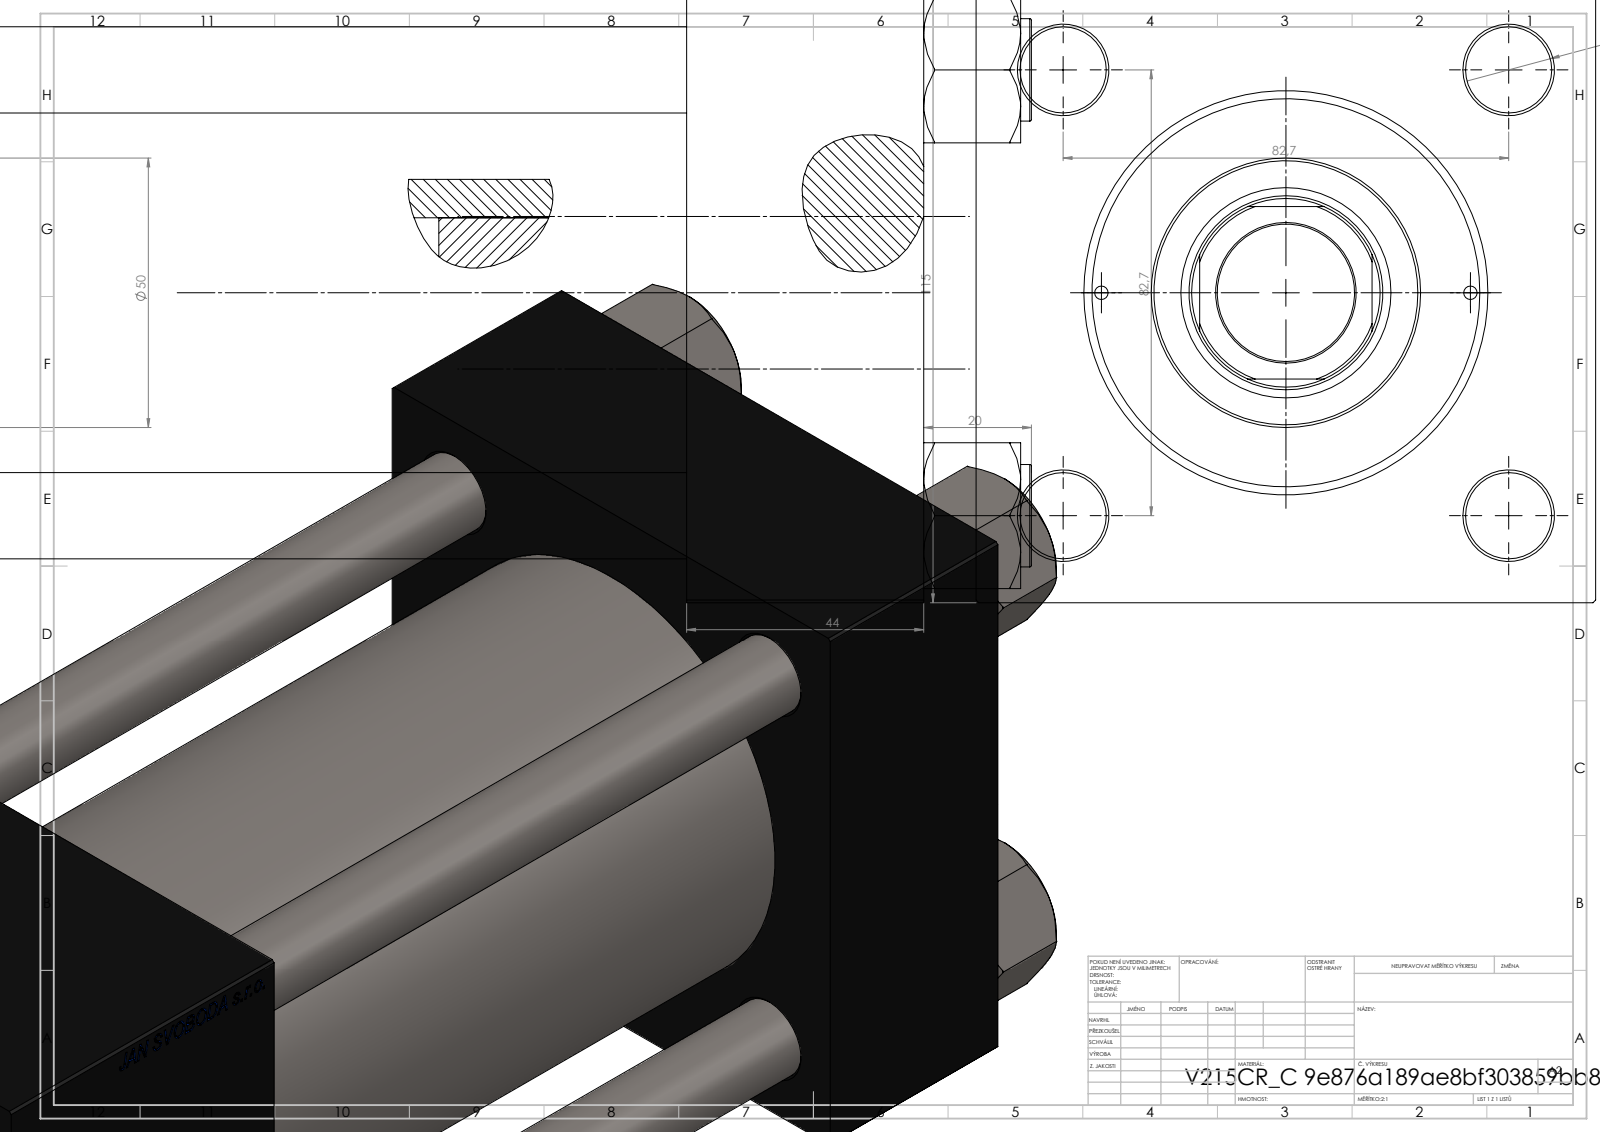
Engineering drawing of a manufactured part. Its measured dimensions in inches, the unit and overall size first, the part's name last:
Units: inches
Overall size (bounding box): 12.205 × 4.528 × 4.528
Round holes (diameter × count): ⌀0.63 ×4, ⌀0.098 ×2, ⌀0.276 ×2, ⌀1.041 ×2, ⌀1.378 ×2, ⌀1.004 ×1, ⌀1.417 ×1, ⌀1.535 ×1, ⌀2.402 ×1, ⌀2.835 ×1, ⌀3.15 ×1
Round bosses / shafts (diameter × count): ⌀0.748 ×4, ⌀3.386 ×1, ⌀1.969 ×1
Partial cylindrical surfaces — rounded edges, fillets, slot ends (radius × count): R0.689 ×1
Main face-to-face distances: 4.528, 1.732, 10.197, 8.465, 7.48, 5.748, 2.717, 3.937, 9.067, 7.335
Hole centre spacings: 1.652, 2.302, 3.256, 3.393, 1.348, 4.605, 2.697, 7.52
Volume: 121.7 in³ · Surface area: 519.8 in²
Bodies: 11 solids, 1202 faces (576 planar, 90 cylindrical, 536 other)
Part name (STEP PRODUCT): V215CR_C_Body; V215_VC_A; NUT_M5_C; V215CR_VCP_C (+1 more)
STEP written by: SolidWorks 2019 (CONFIG_CONTROL_DESIGN)
